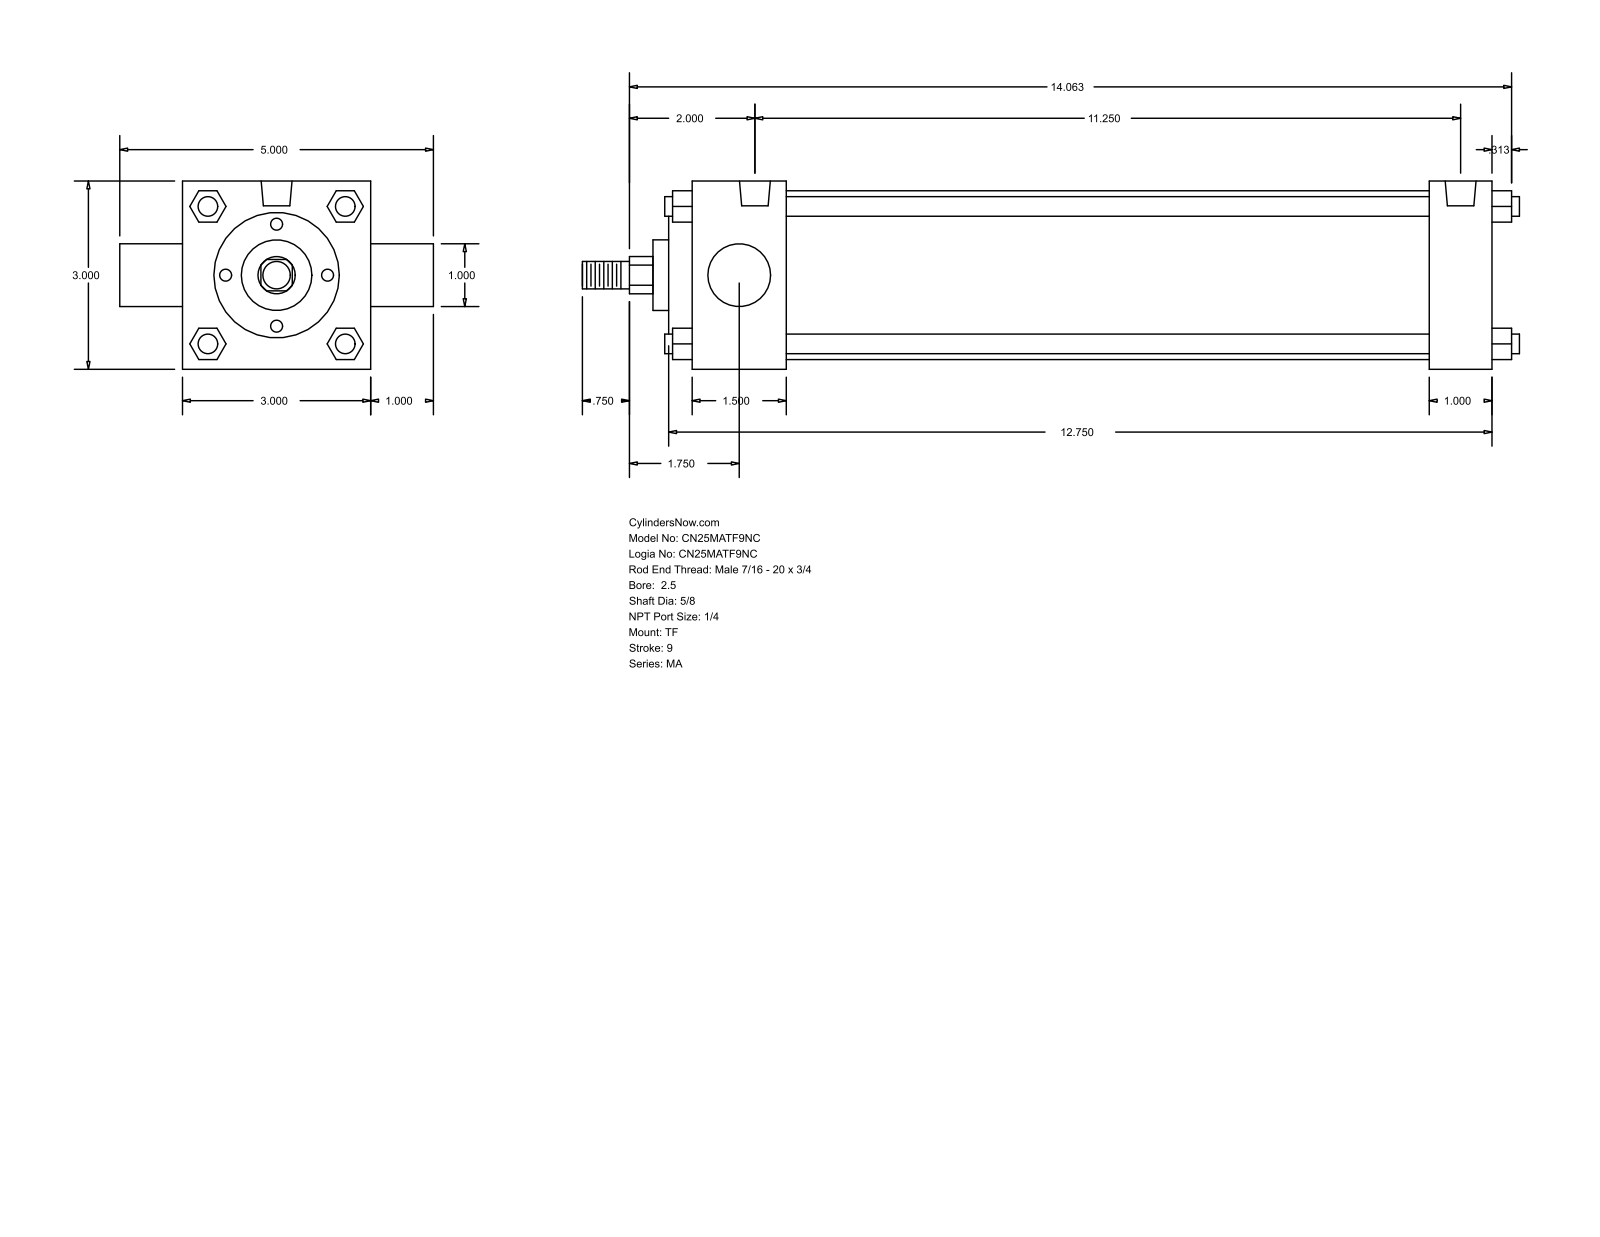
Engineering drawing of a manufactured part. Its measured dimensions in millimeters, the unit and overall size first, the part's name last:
Units: millimetres
Overall size (bounding box): 379.41 × 127 × 76.2
Round holes (diameter × count): ⌀7.94 ×3, ⌀12.49 ×2
Round bosses / shafts (diameter × count): ⌀7.94 ×4, ⌀68.33 ×1, ⌀50.8 ×1, ⌀28.57 ×1, ⌀25.4 ×1, ⌀15.88 ×1, ⌀11.11 ×1
Partial cylindrical surfaces — rounded edges, fillets, slot ends (radius × count): R7.54 ×1
Main face-to-face distances: 76.2, 323.85, 25.4, 38.1, 298.45, 260.35, 285.75, 12.7, 9.52, 47.62
Hole centre spacings: 285.75
Bodies: 0 solids, 122 faces (93 planar, 29 cylindrical, 0 other)
Part name (STEP PRODUCT): MA_TF__0250_0.625
STEP written by: GSSL Pune (CONFIG_CONTROL_DESIGN)
